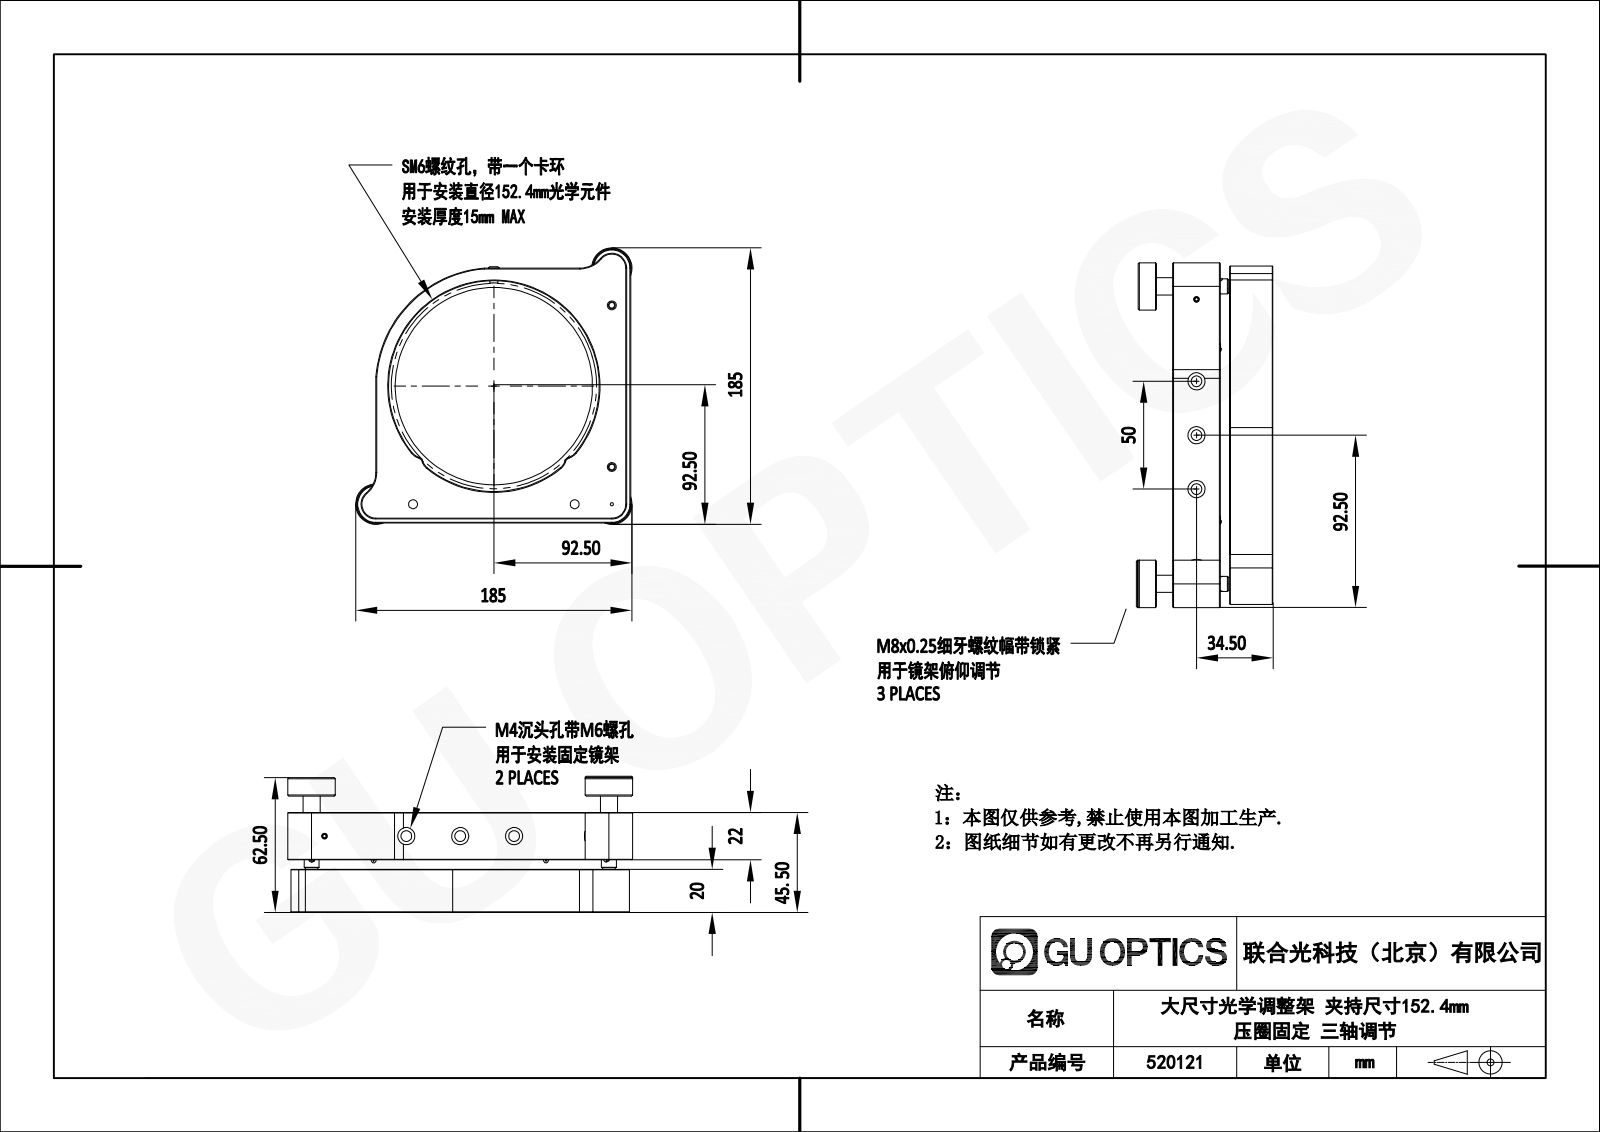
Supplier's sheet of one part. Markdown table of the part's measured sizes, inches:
| quantity | value |
| --- | --- |
| STEP written by | SolidWorks 2021 (CONFIG_CONTROL_DESIGN) |
| units | inches |
| bodies | 0 solids, 404 faces (107 planar, 201 cylindrical, 96 other) |
| overall size | 7.283 × 7.283 × 2.49 |
| round holes (diameter × count) | 0.315 × 12, 0.13 × 6, 0.197 × 6, 0.236 × 3, 0.472 × 3, 0.059 × 2, 0.098 × 2, 5.748 × 1, 5.803 × 1, 6 × 1, 6.039 × 1 |
| round bosses / shafts (diameter × count) | 0.079 × 6, 0.866 × 3, 0.315 × 3, 0.512 × 1 |
| partial cylindrical surfaces (radius × count) | 0.041 × 12, 0.118 × 8, 0.236 × 4, 0.374 × 3, 0.984 × 2, 1.102 × 2, 1.181 × 2, 3.071 × 1 |
| main face-to-face distances | 0.787, 0.866, 0.138, 0.059, 0.925, 1.004, 1.791, 0.65, 0.591, 0.63 |
| hole center spacings | 0.984, 4.538, 0.846, 1.181, 1.831, 1.969, 1.988, 2.972 |
